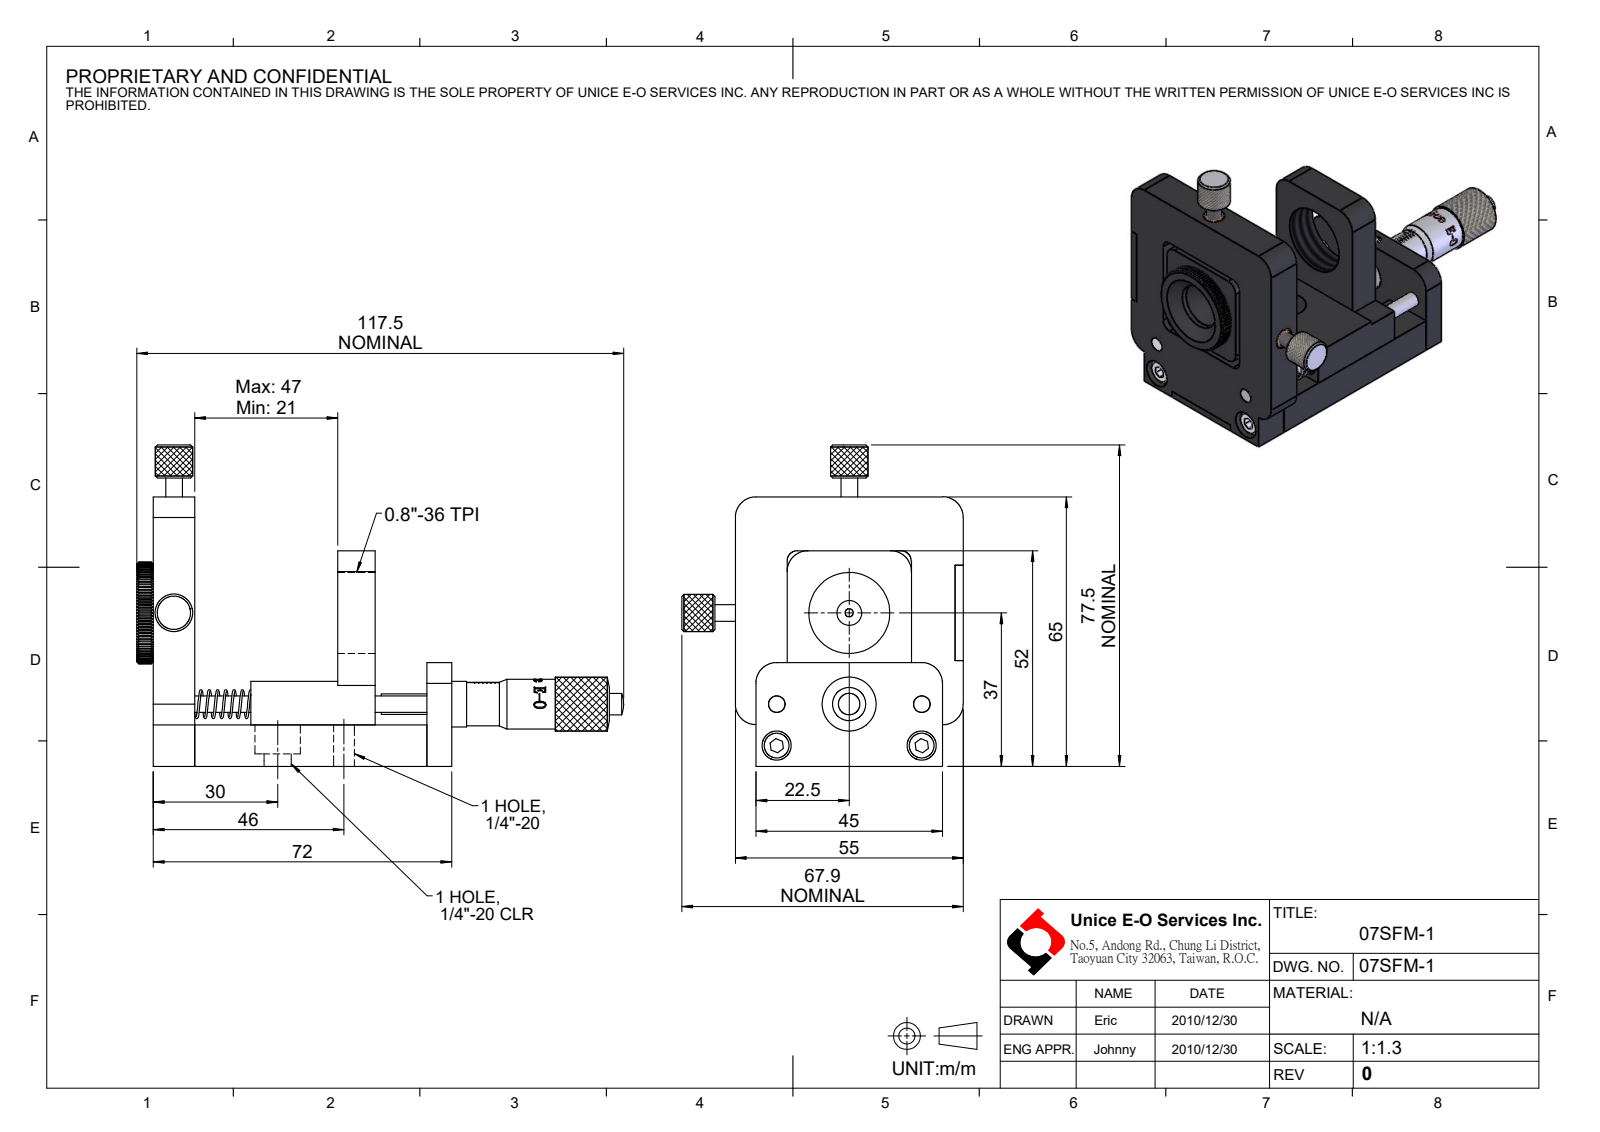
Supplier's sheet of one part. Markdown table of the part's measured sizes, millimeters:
| quantity | value |
| --- | --- |
| part name | 07SFM-1 |
| STEP written by | SolidWorks 2016 (CONFIG_CONTROL_DESIGN) |
| units | millimeters |
| bodies | 39 solids, 1407 faces (627 planar, 341 cylindrical, 439 other) |
| overall size | 117.52 × 77.52 × 67.91 |
| volume | 81 432 mm³ |
| surface area | 50 776 mm² |
| round holes (diameter × count) | 4.5 × 8, 2.5 × 7, 6 × 5, 8 × 4, 3.2 × 2, 3.3 × 2, 4 × 2, 9.5 × 2, 1.6 × 1, 3.4 × 1, 5 × 1, 5.11 × 1 |
| round bosses / shafts (diameter × count) | 6 × 4, 4 × 4, 9 × 2, 7 × 2, 23 × 1, 21 × 1, 13 × 1, 12 × 1 |
| partial cylindrical surfaces (radius × count) | 5 × 8, 1.5 × 4, 2.5 × 4, 3 × 4, 5.98 × 1, 12.25 × 1 |
| main face-to-face distances | 10, 5, 66, 2, 6, 3, 56, 50, 10.5, 9.5 |
| hole center spacings | 7.5, 8.5, 10, 15, 17, 17.5, 20.16, 26.1 |
